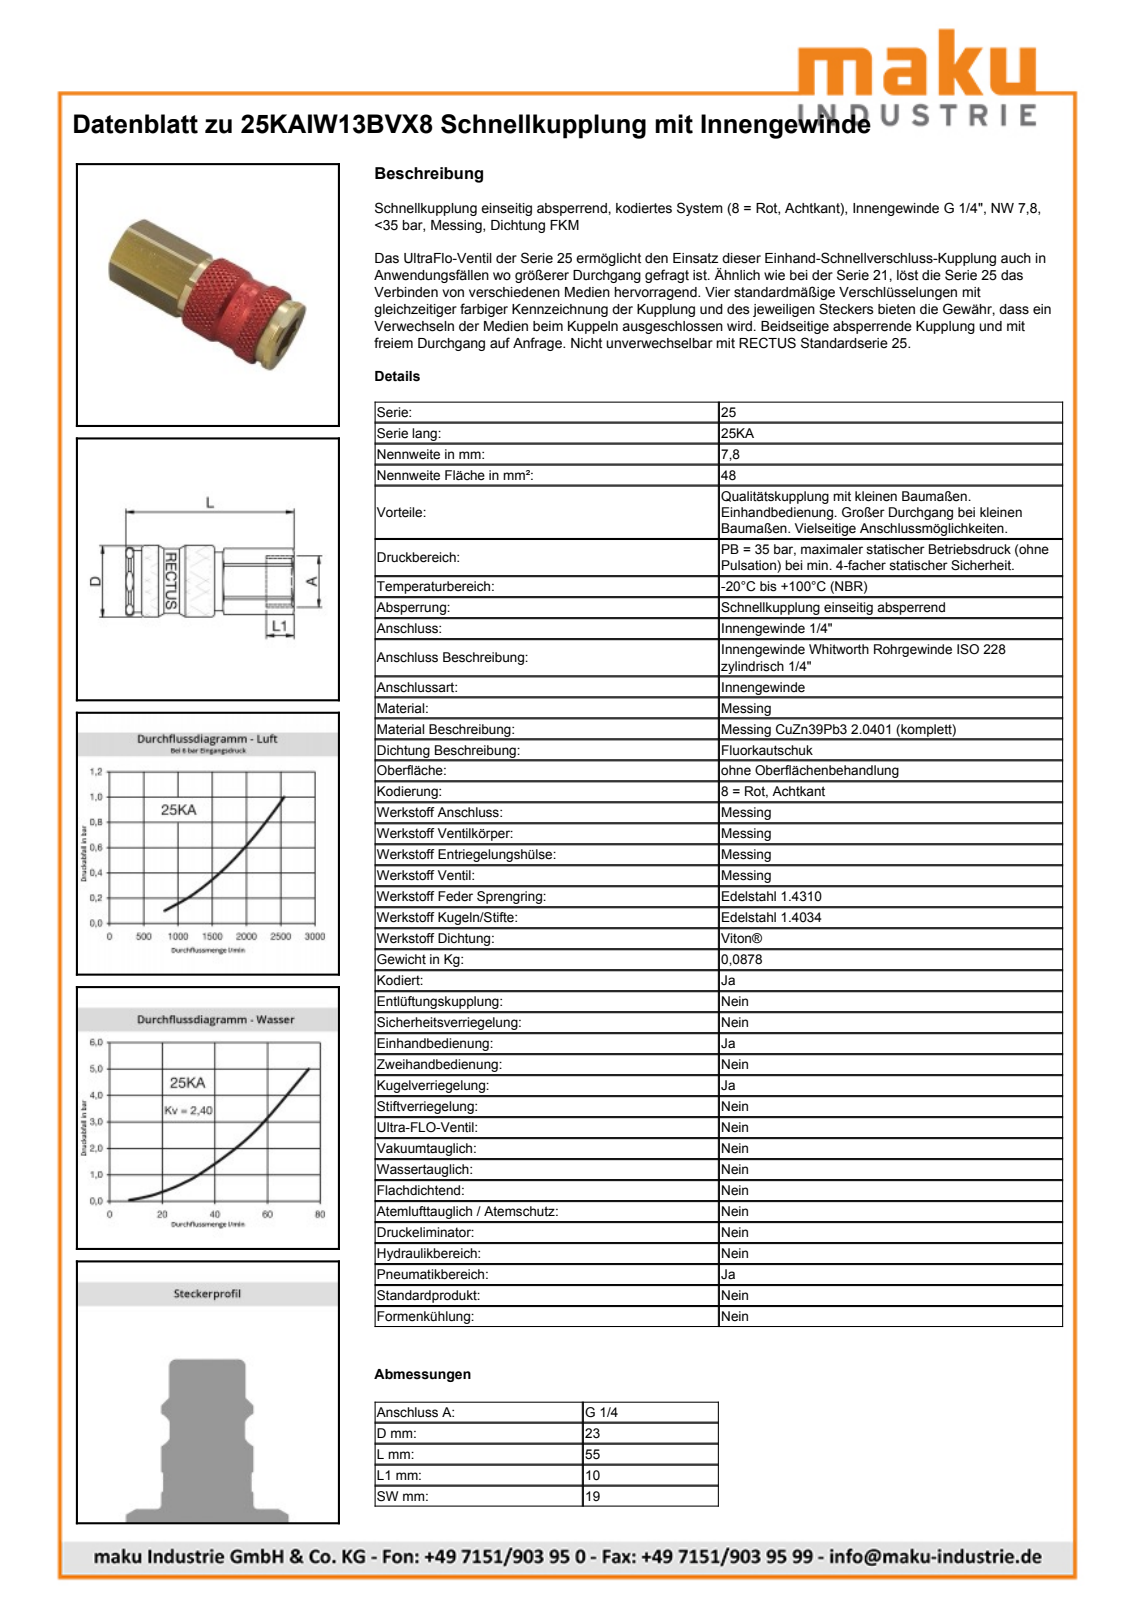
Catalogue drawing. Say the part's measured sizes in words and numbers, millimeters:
The part is named "25KAIW13BPX8". Its 3-D file was written by "Autodesk Inventor 2019 (AUTOMOTIVE_DESIGN)". It is 4 solids with 708 faces: 243 planar, 86 cylindrical and 379 other. Overall it measures 55.5 by 23.15 by 23.15 millimeters. Its volume is 17 854 cubic millimeters and its surface area 12 696 square millimeters. Round holes: 1 of diameter 11.45, 1 of diameter 12.1, 1 of diameter 12.5, 1 of diameter 14, 1 of diameter 14.1, 1 of diameter 15.1, 1 of diameter 17.25, 1 of diameter 19.35, 1 of diameter 20.05. Round bosses or shafts: 1 of diameter 23.15, 1 of diameter 21, 1 of diameter 20, 1 of diameter 18.95, 1 of diameter 16, 1 of diameter 15.3, 1 of diameter 15.26. Partial cylindrical surfaces (rounded edges, fillets, slot ends): 1 of radius 7.9, 1 of radius 10.4, 1 of radius 10.7, 1 of radius 11. The main face-to-face distances are 19, 39.3, 6.2, 45.5, 55.5, 49.3, 10, 21, 16.75, 24.5.
